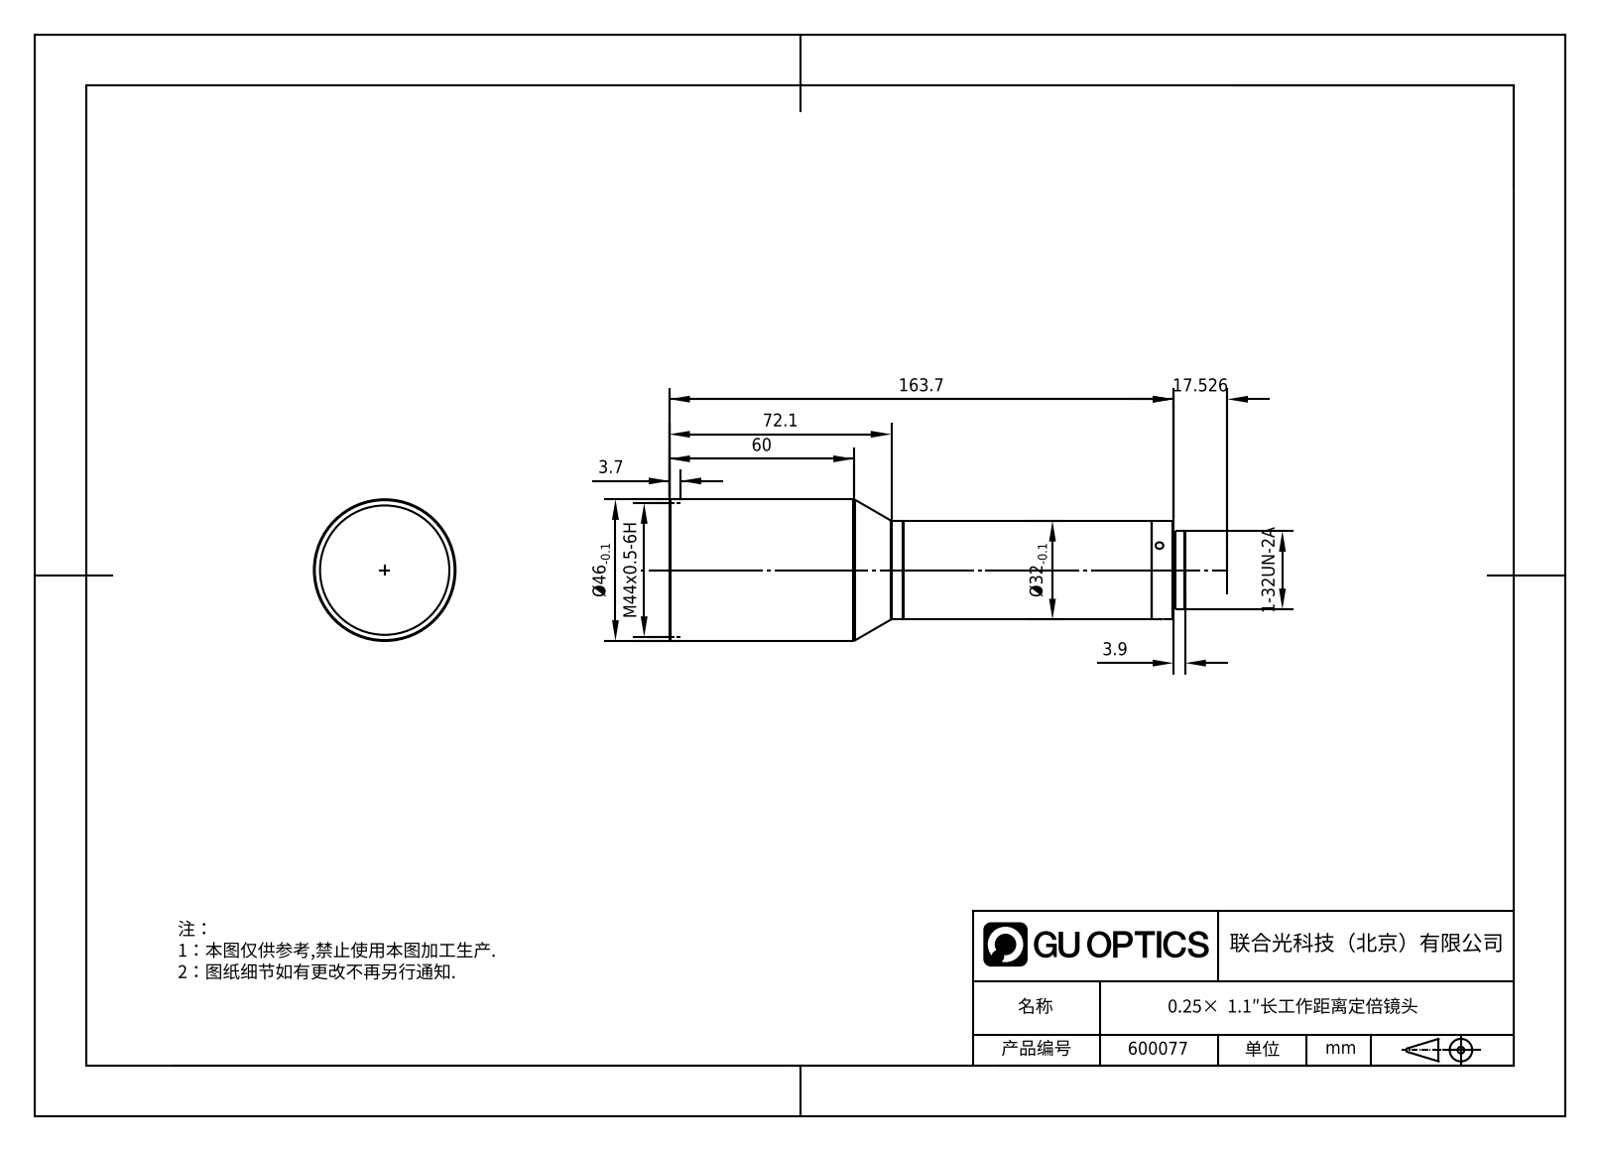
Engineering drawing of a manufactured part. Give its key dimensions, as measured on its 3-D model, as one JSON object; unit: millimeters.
{"part_name": "600077", "step_written_by": "SolidWorks 2020 (CONFIG_CONTROL_DESIGN)", "units": "millimeters", "bodies": {"solids": 1, "faces": 34, "planar": 9, "cylindrical": 16, "other": 9}, "overall_size": [167.63, 46, 46], "volume_mm3": 183947, "surface_area_mm2": 26585, "round_holes": [[2.5, 3], [42, 1]], "round_bosses_or_shafts": [[46, 1], [32, 1], [25.4, 1], [24.6, 1]], "partial_cylinders_radius": [[11.82, 1], [14.62, 1]], "face_to_face_distances": [158.64, 158.74, 3.9, 154.74, 154.84, 167.64, 163.74, 9, 8.9, 3.1]}
